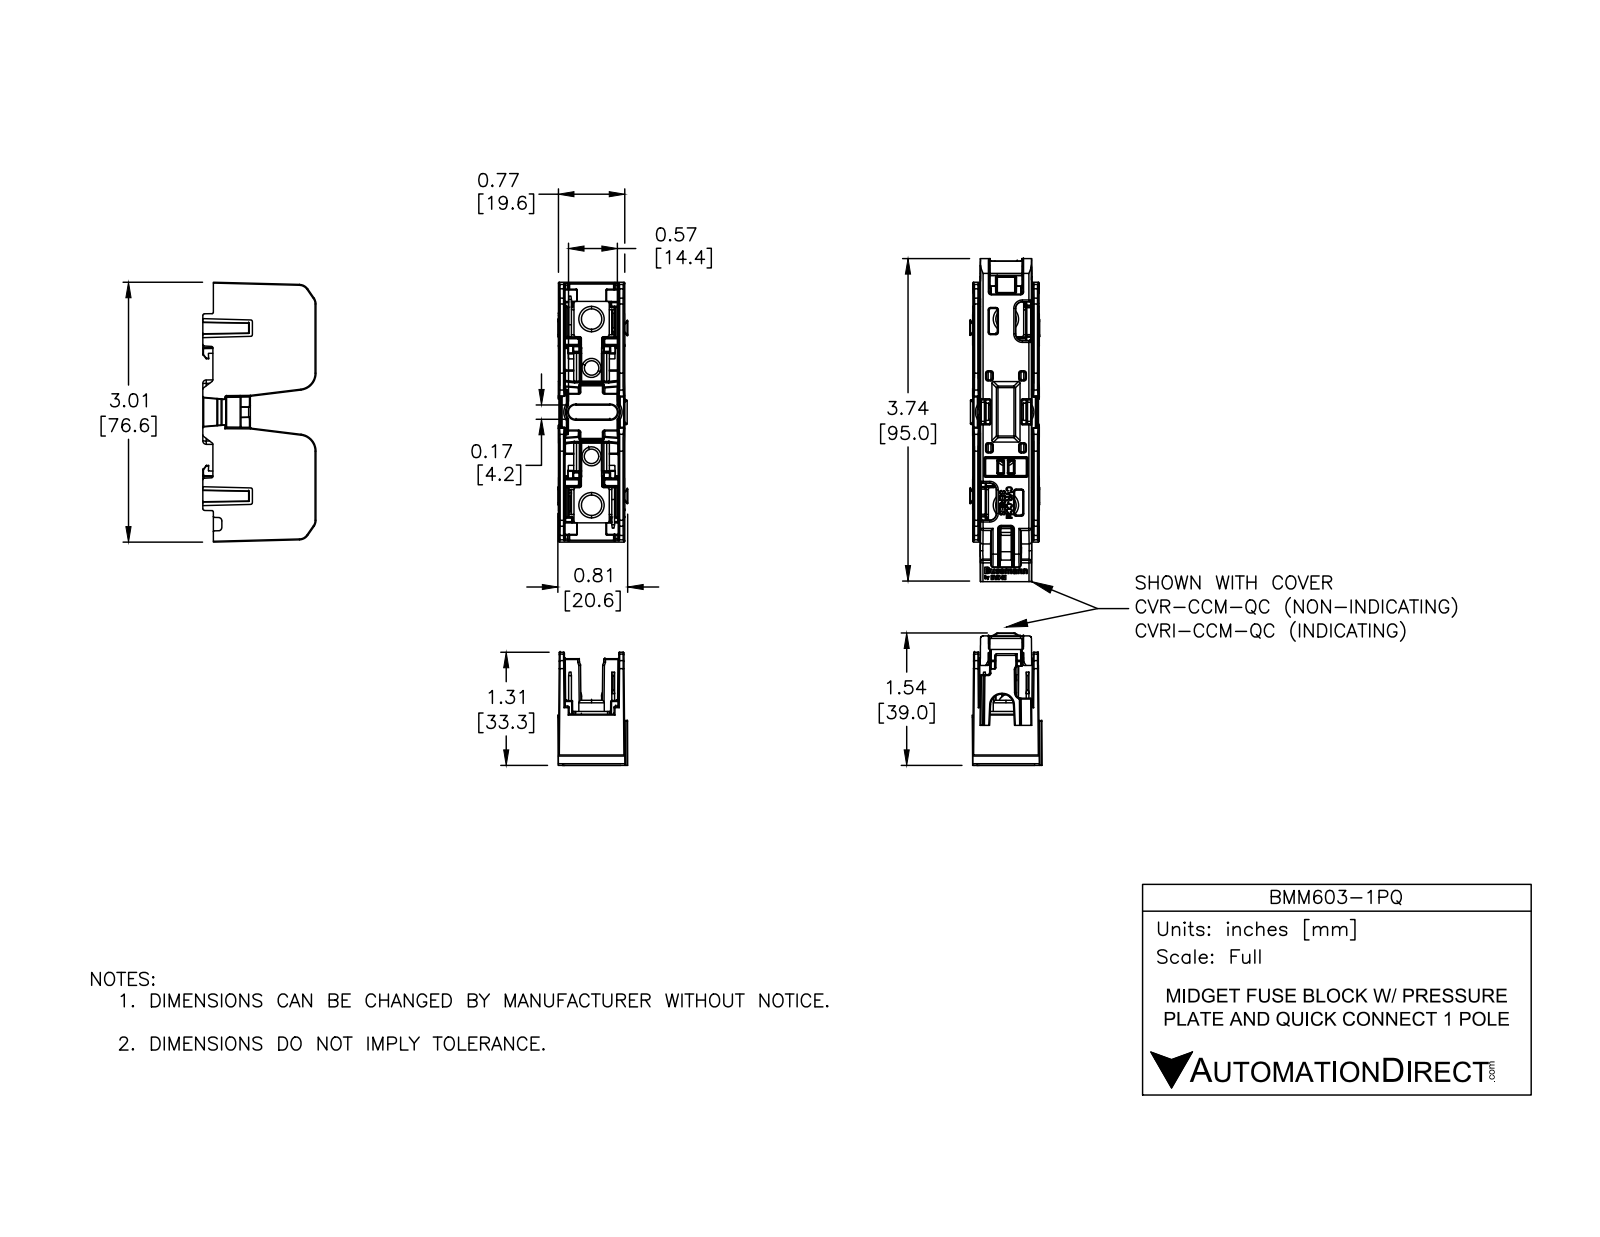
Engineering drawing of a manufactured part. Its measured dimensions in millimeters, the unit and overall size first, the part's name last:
Units: millimetres
Overall size (bounding box): 76.6 × 33.3 × 20.6
Round holes (diameter × count): ⌀1.9 ×4, ⌀3.6 ×2
Round bosses / shafts (diameter × count): ⌀7.5 ×2, ⌀5.6 ×2, ⌀3.5 ×2
Partial cylindrical surfaces — rounded edges, fillets, slot ends (radius × count): R0.1 ×12, R0.5 ×12, R0.3 ×4, R3 ×4, R0.8 ×2, R1.3 ×2, R1.5 ×2, R2.1 ×2
Main face-to-face distances: 17.6, 17.6, 15.1, 0.8, 12, 14.9, 1.5, 3.1, 2.5, 27.6
Hole centre spacings: 3, 56.7, 26, 53.9, 59.4
Volume: 20 400 mm³ · Surface area: 16 830 mm²
Bodies: 5 solids, 493 faces (344 planar, 95 cylindrical, 54 other)
Part name (STEP PRODUCT): BMM603-1PQ
STEP written by: SolidWorks 2021 (CONFIG_CONTROL_DESIGN)
